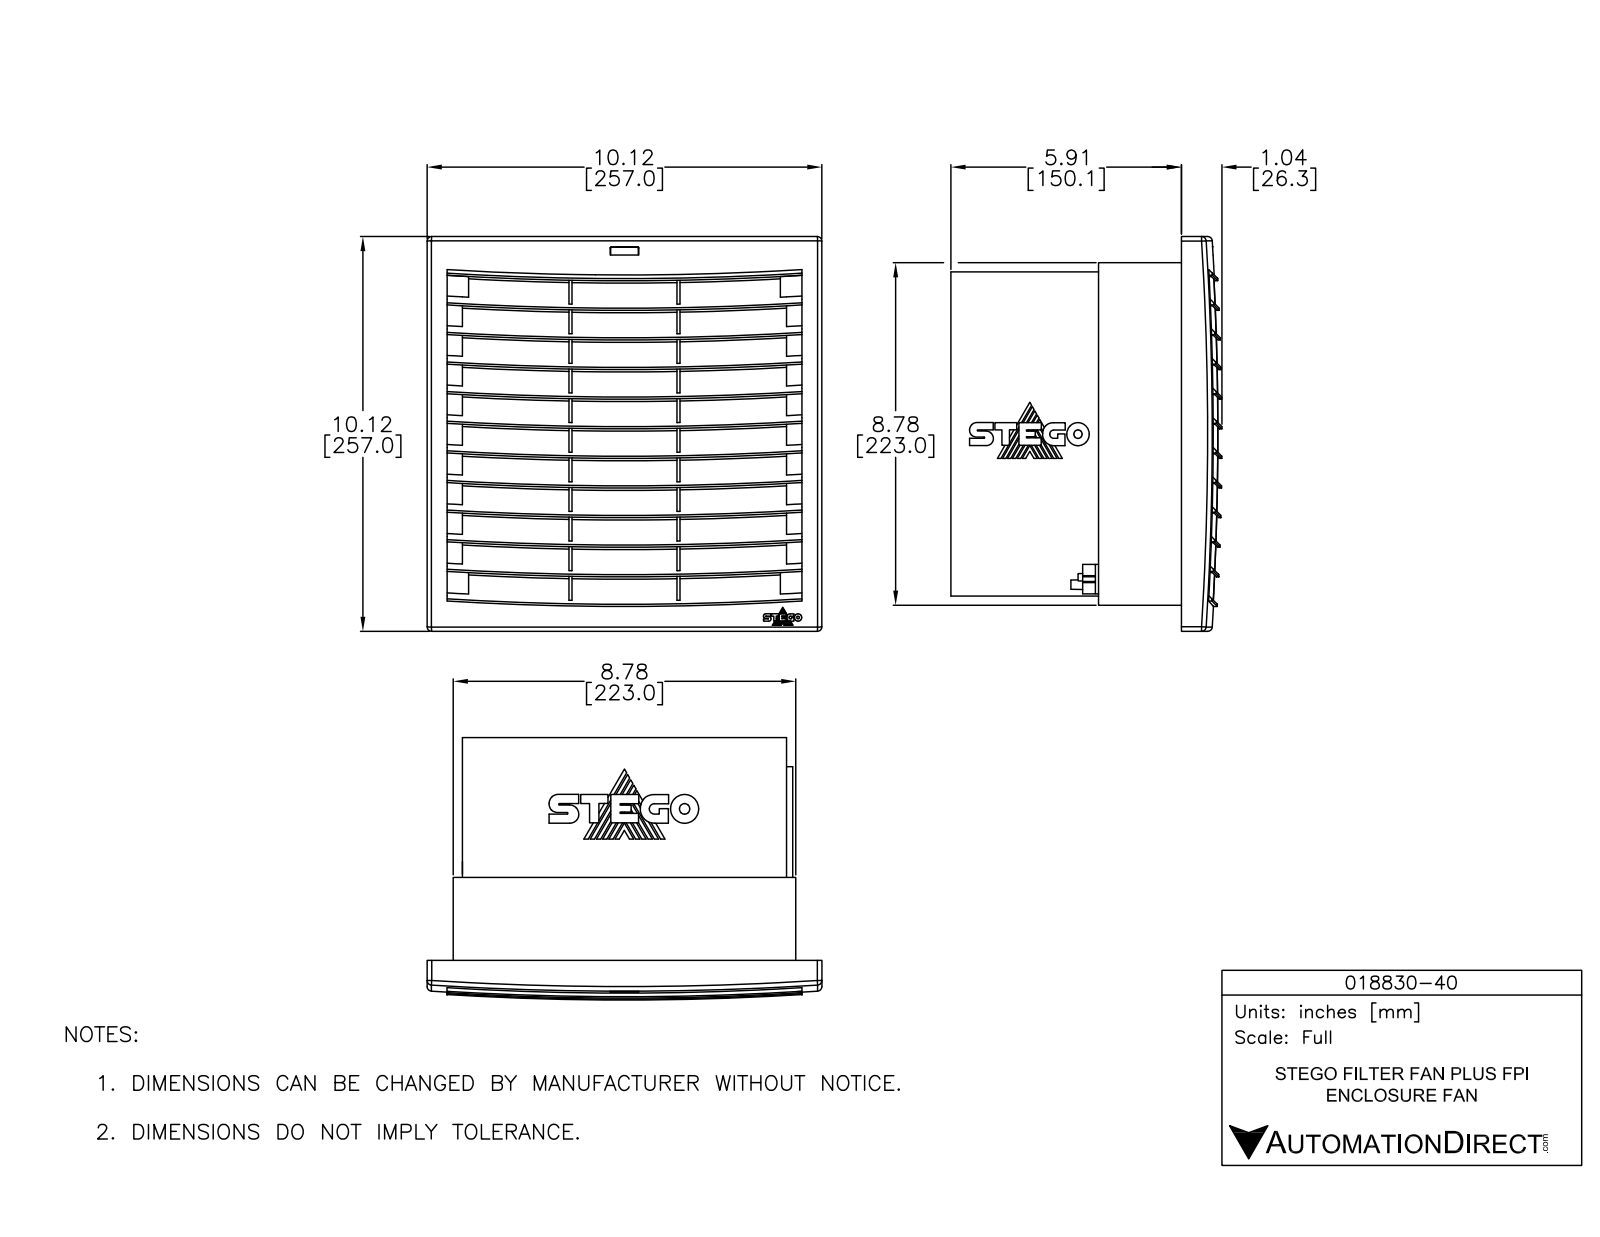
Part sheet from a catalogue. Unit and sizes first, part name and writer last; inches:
Units: inches
Overall size (bounding box): 10.118 × 10.118 × 6.811
Round holes (diameter × count): ⌀2.268 ×1, ⌀3.018 ×1, ⌀3.769 ×1, ⌀4.487 ×1, ⌀4.52 ×1, ⌀5.27 ×1, ⌀5.42 ×1, ⌀6.021 ×1, ⌀6.353 ×1, ⌀6.929 ×1, ⌀7.463 ×1
Round bosses / shafts (diameter × count): ⌀8.64 ×1, ⌀8.228 ×1, ⌀8.146 ×1, ⌀6.707 ×1, ⌀6.336 ×1, ⌀5.774 ×1, ⌀5.585 ×1, ⌀4.841 ×1
Partial cylindrical surfaces — rounded edges, fillets, slot ends (radius × count): R42.577 ×21, R3.361 ×5, R0.197 ×4, R0.26 ×4, R0.933 ×1, R1.311 ×1, R1.488 ×1, R1.777 ×1
Main face-to-face distances: 0.536, 0.059, 2.145, 2.681, 1.609, 0.22, 8.56, 1.073, 1.072, 0.477
Volume: 155 in³ · Surface area: 918.5 in²
Bodies: 1 solid, 808 faces (462 planar, 346 cylindrical, 0 other)
Part name (STEP PRODUCT): 018830-40
STEP written by: SolidWorks 2018 (AUTOMOTIVE_DESIGN)
